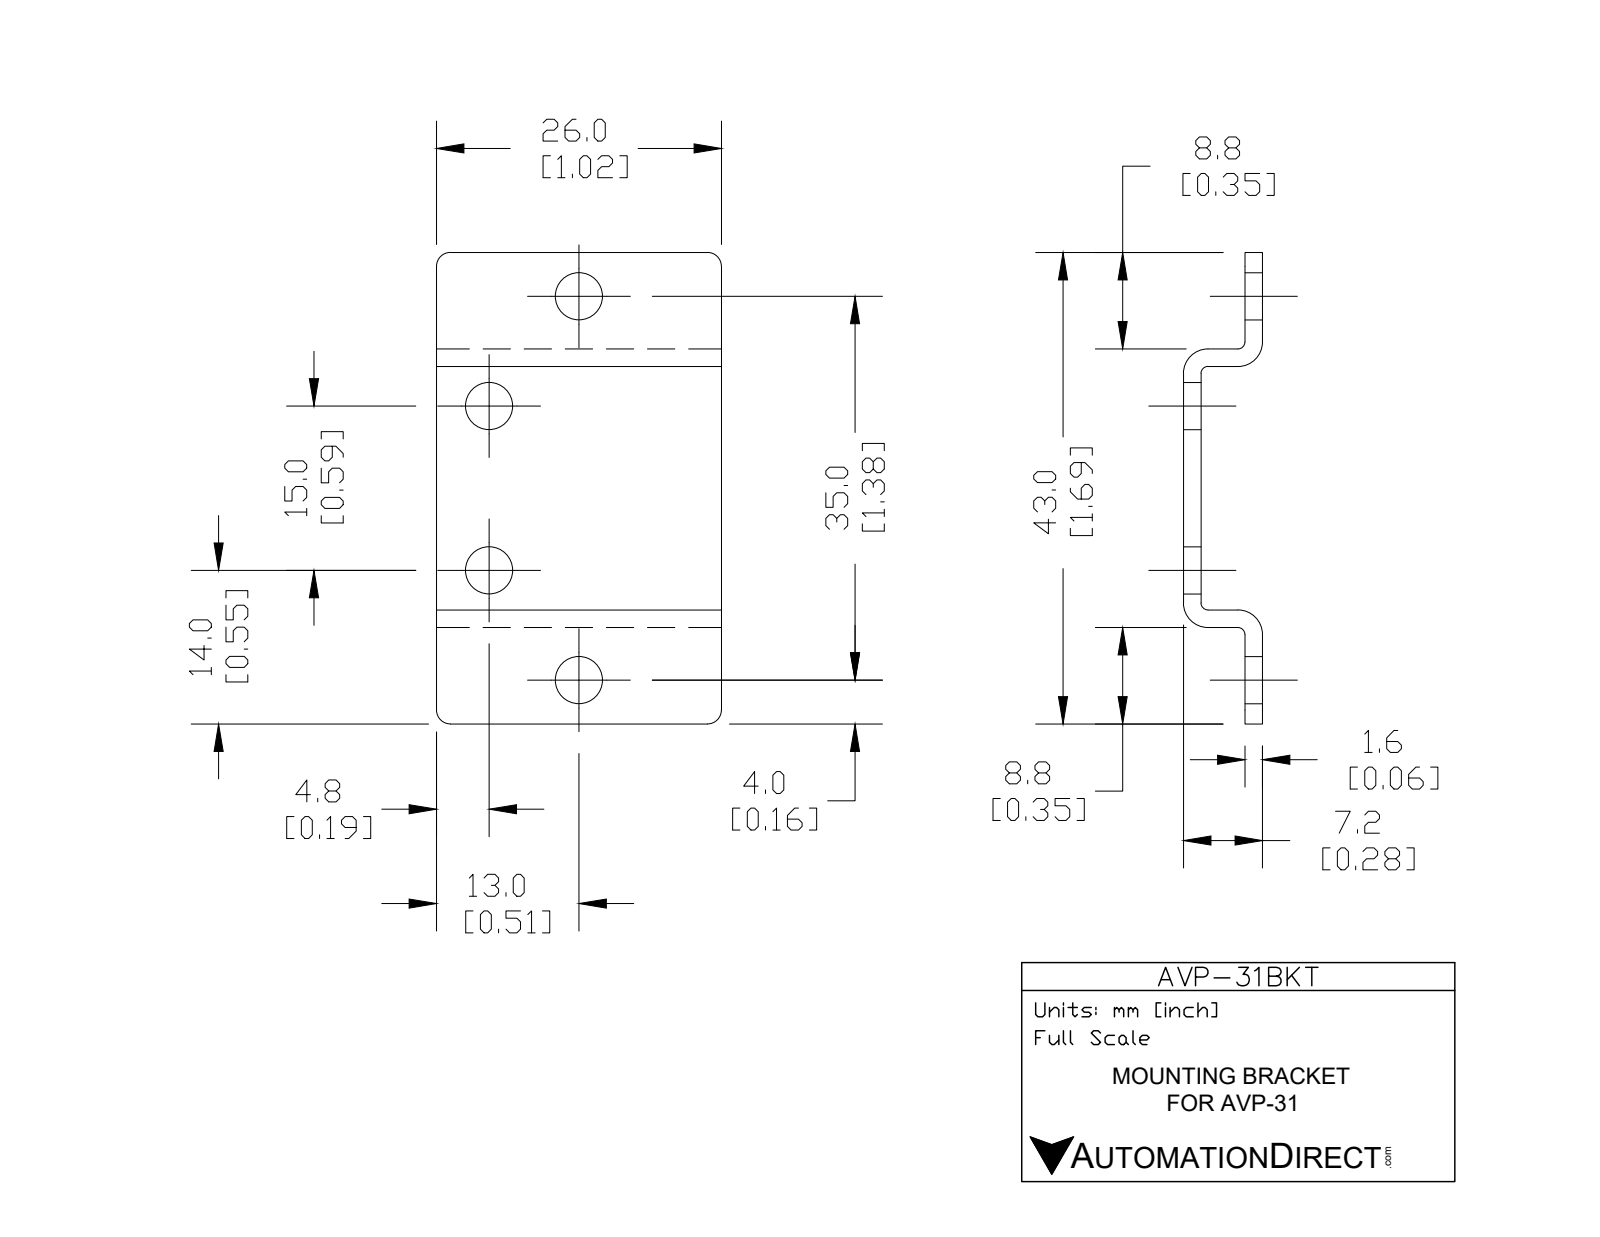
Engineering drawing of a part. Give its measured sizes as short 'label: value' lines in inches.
name: AVP-31BKT
written by: SolidWorks 2017 (AUTOMOTIVE_DESIGN)
unit: in
bodies: 1 solid, 50 faces (30 planar, 20 cylindrical, 0 other)
size: 1.693 × 1.024 × 0.283
volume: 0.126 in³; area: 4.504 in²
holes: 4× ⌀0.169
rounds: 4× R0.024, 4× R0.051, 4× R0.087
face distances: 0.063, 0.22, 0.157, 0.283, 0.937, 1.024, 0.346, 0.409, 1.283, 1.346
hole spacings: 0.509, 1.036, 0.591, 1.378
